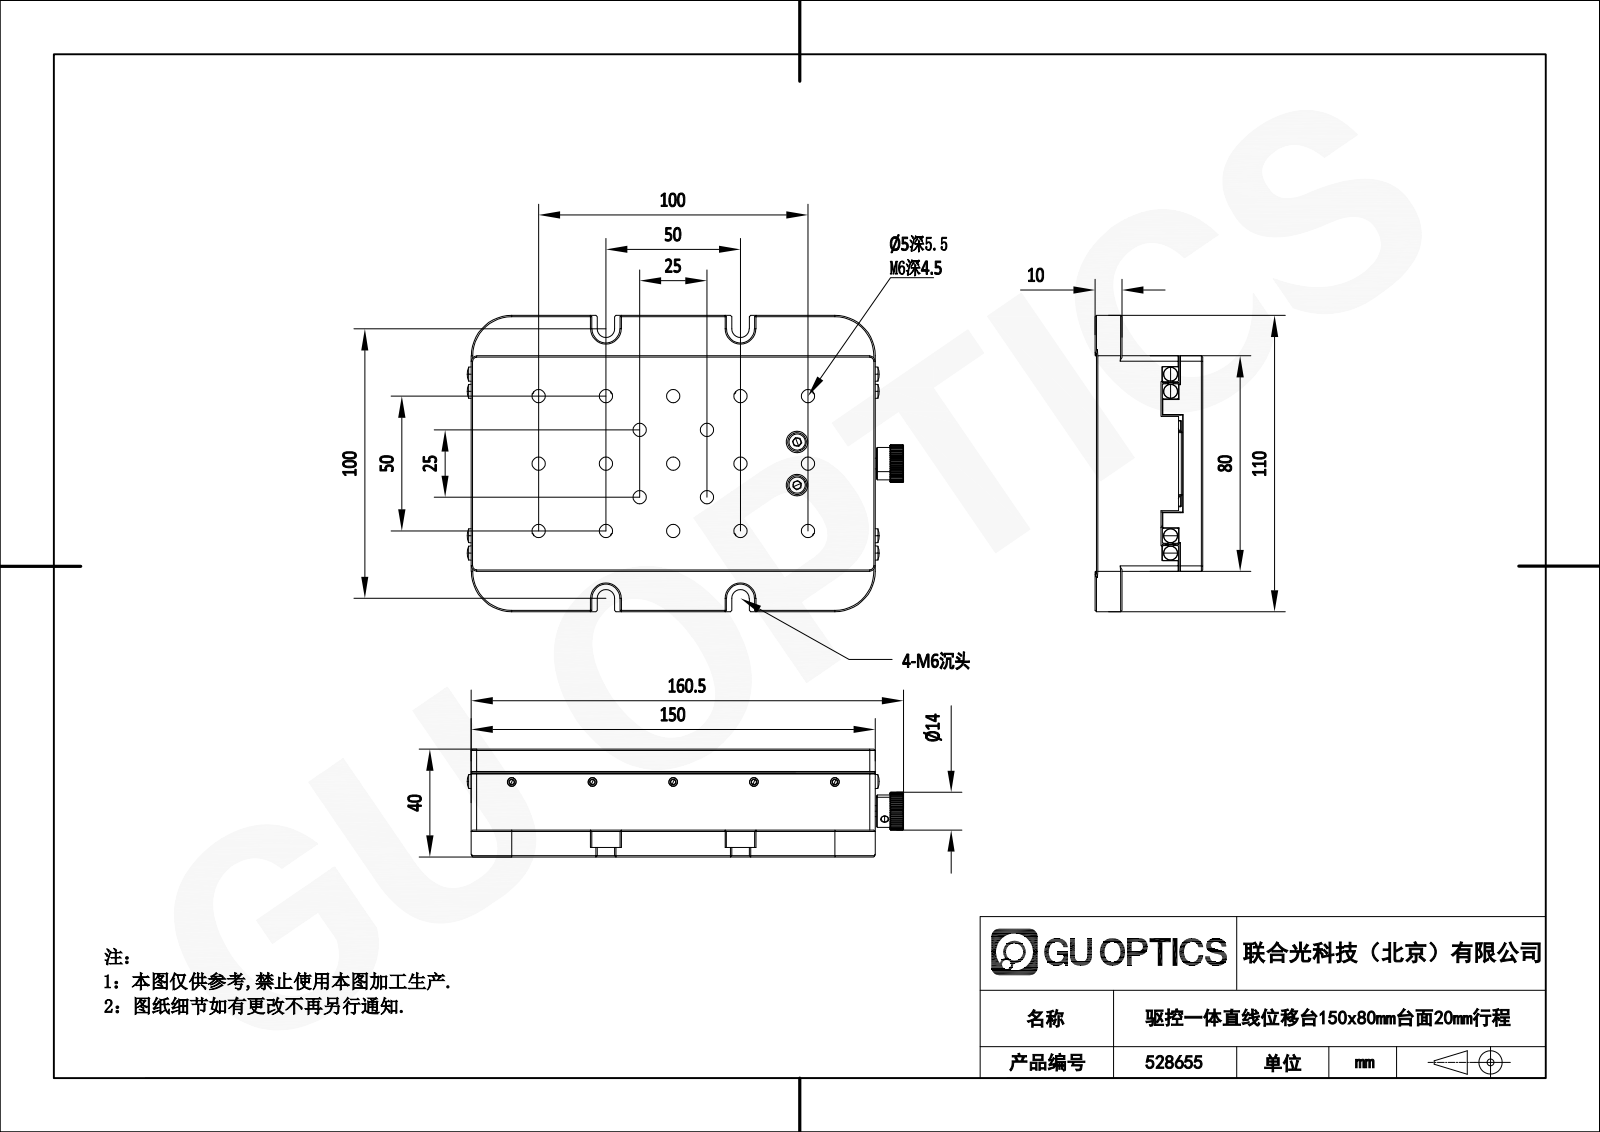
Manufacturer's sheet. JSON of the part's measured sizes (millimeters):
{"part_name": "528655", "step_written_by": "SolidWorks 2020 (CONFIG_CONTROL_DESIGN)", "units": "millimeters", "bodies": {"solids": 89, "faces": 4273, "planar": 2170, "cylindrical": 1065, "other": 1038}, "overall_size": [162, 110, 40], "volume_mm3": 375625, "surface_area_mm2": 160739, "round_holes": [[4.4, 44], [2.55, 40], [3.5, 24], [6, 23], [1.5, 20], [5, 20], [2.5, 11], [3.3, 11], [2.05, 8], [2, 6], [3.4, 6], [4.5, 6]], "round_bosses_or_shafts": [[2, 76], [5.5, 26], [3, 26], [3.8, 22], [4, 7], [2.2, 4], [7, 2], [22, 1]], "partial_cylinders_radius": [[2, 36], [1, 10], [0.5, 8], [1.75, 8], [1.3, 4], [3.25, 4], [5.25, 4], [15, 4]], "face_to_face_distances": [7.5, 15, 6, 24.5, 6.5, 0.5, 39.5, 4, 9.5, 9], "hole_center_spacings": [25, 39.53, 55.9, 35.36, 17.68, 50, 75, 53.03]}
